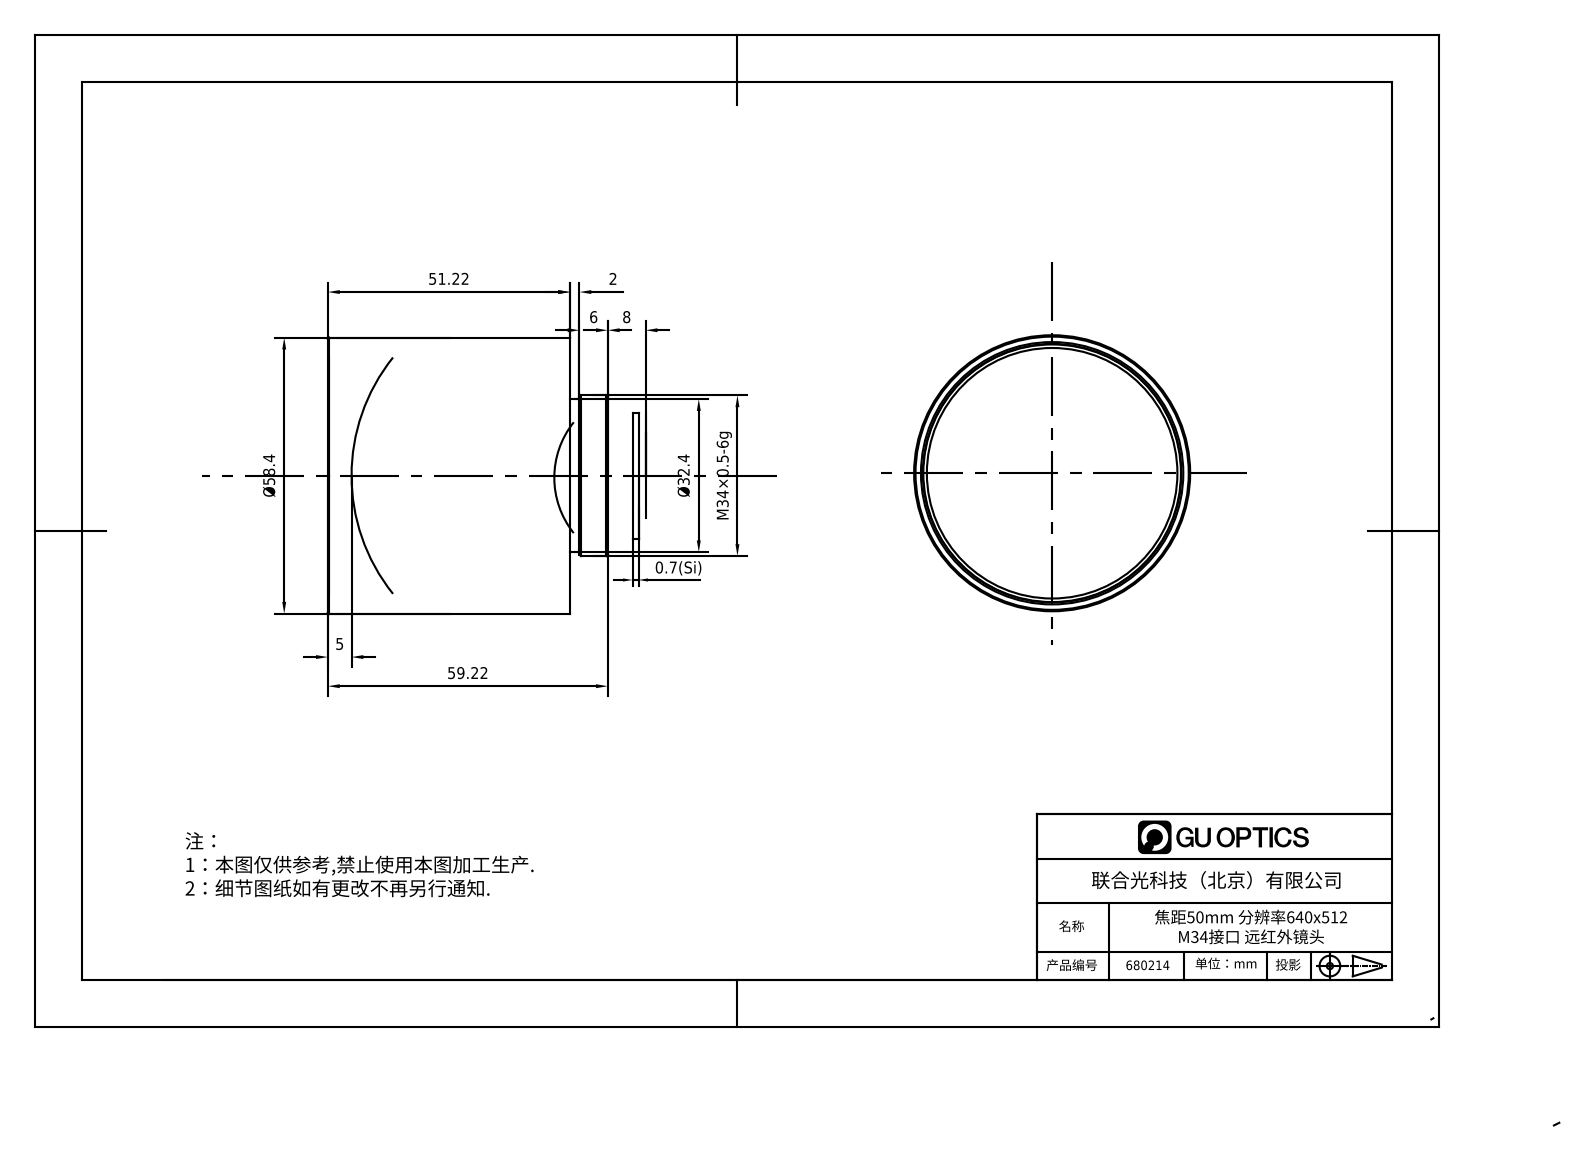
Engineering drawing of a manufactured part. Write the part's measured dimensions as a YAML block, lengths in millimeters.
part_name: "50mm"
step_written_by: "SolidWorks 2020 (CONFIG_CONTROL_DESIGN)"
units: millimeters
bodies: {solids: 1, faces: 26, planar: 9, cylindrical: 10, other: 7}
overall_size: [59.22, 58.4, 58.4]
volume: 117145
surface_area: 19149
round_holes:
  - {diameter: 19, count: 1}
  - {diameter: 53, count: 1}
  - {diameter: 54.5, count: 1}
  - {diameter: 54.7, count: 1}
  - {diameter: 55.5, count: 1}
  - {diameter: 55.9, count: 1}
round_bosses_or_shafts:
  - {diameter: 58.4, count: 1}
  - {diameter: 34, count: 1}
  - {diameter: 32.4, count: 1}
face_to_face_distances: [8, 51.22, 59.22, 7.1, 44.12, 52.12, 13.9, 6.8, 37.32, 45.32]
